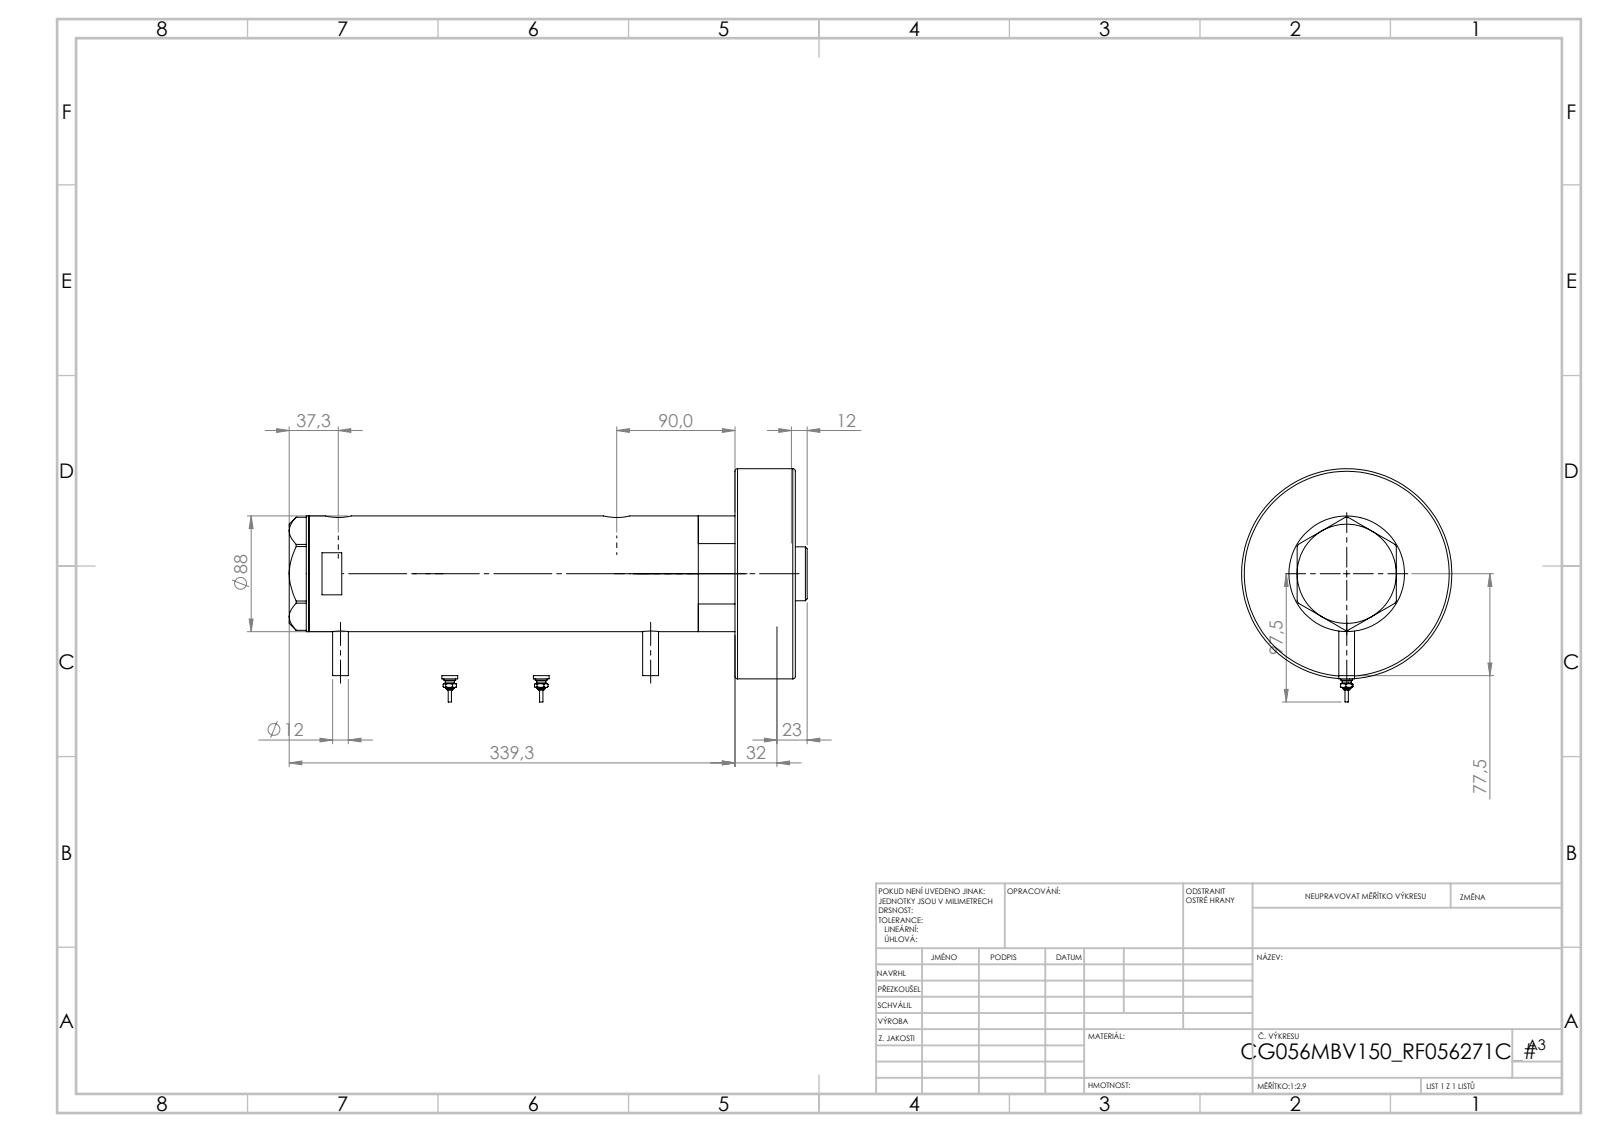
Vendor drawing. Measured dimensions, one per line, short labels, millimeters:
name: V270CG_VC; V270CG_FRONT; V270CG_BACK; V270CG_271C (+2 more)
written by: SolidWorks 2019 (CONFIG_CONTROL_DESIGN)
unit: mm
bodies: 7 solids, 223 faces (82 planar, 73 cylindrical, 68 other)
size: 394.3 × 177.5 × 160
volume: 2 762 000 mm³; area: 347 494 mm²
holes: 2× ⌀12.5, 2× ⌀13.16, 2× ⌀20, 1× ⌀14.5, 1× ⌀42, 1× ⌀43.5, 1× ⌀56, 1× ⌀60, 1× ⌀75, 1× ⌀80
bosses: 4× ⌀12, 2× ⌀9, 2× ⌀7, 2× ⌀4.5, 2× ⌀2.5, 1× ⌀160, 1× ⌀88, 1× ⌀73
face distances: 46, 324.3, 370.3, 234.4, 89.9, 135.9, 344.3, 26, 208.4, 298.3
hole spacings: 1.7, 25.8, 210.3, 212, 236.1, 237.8
